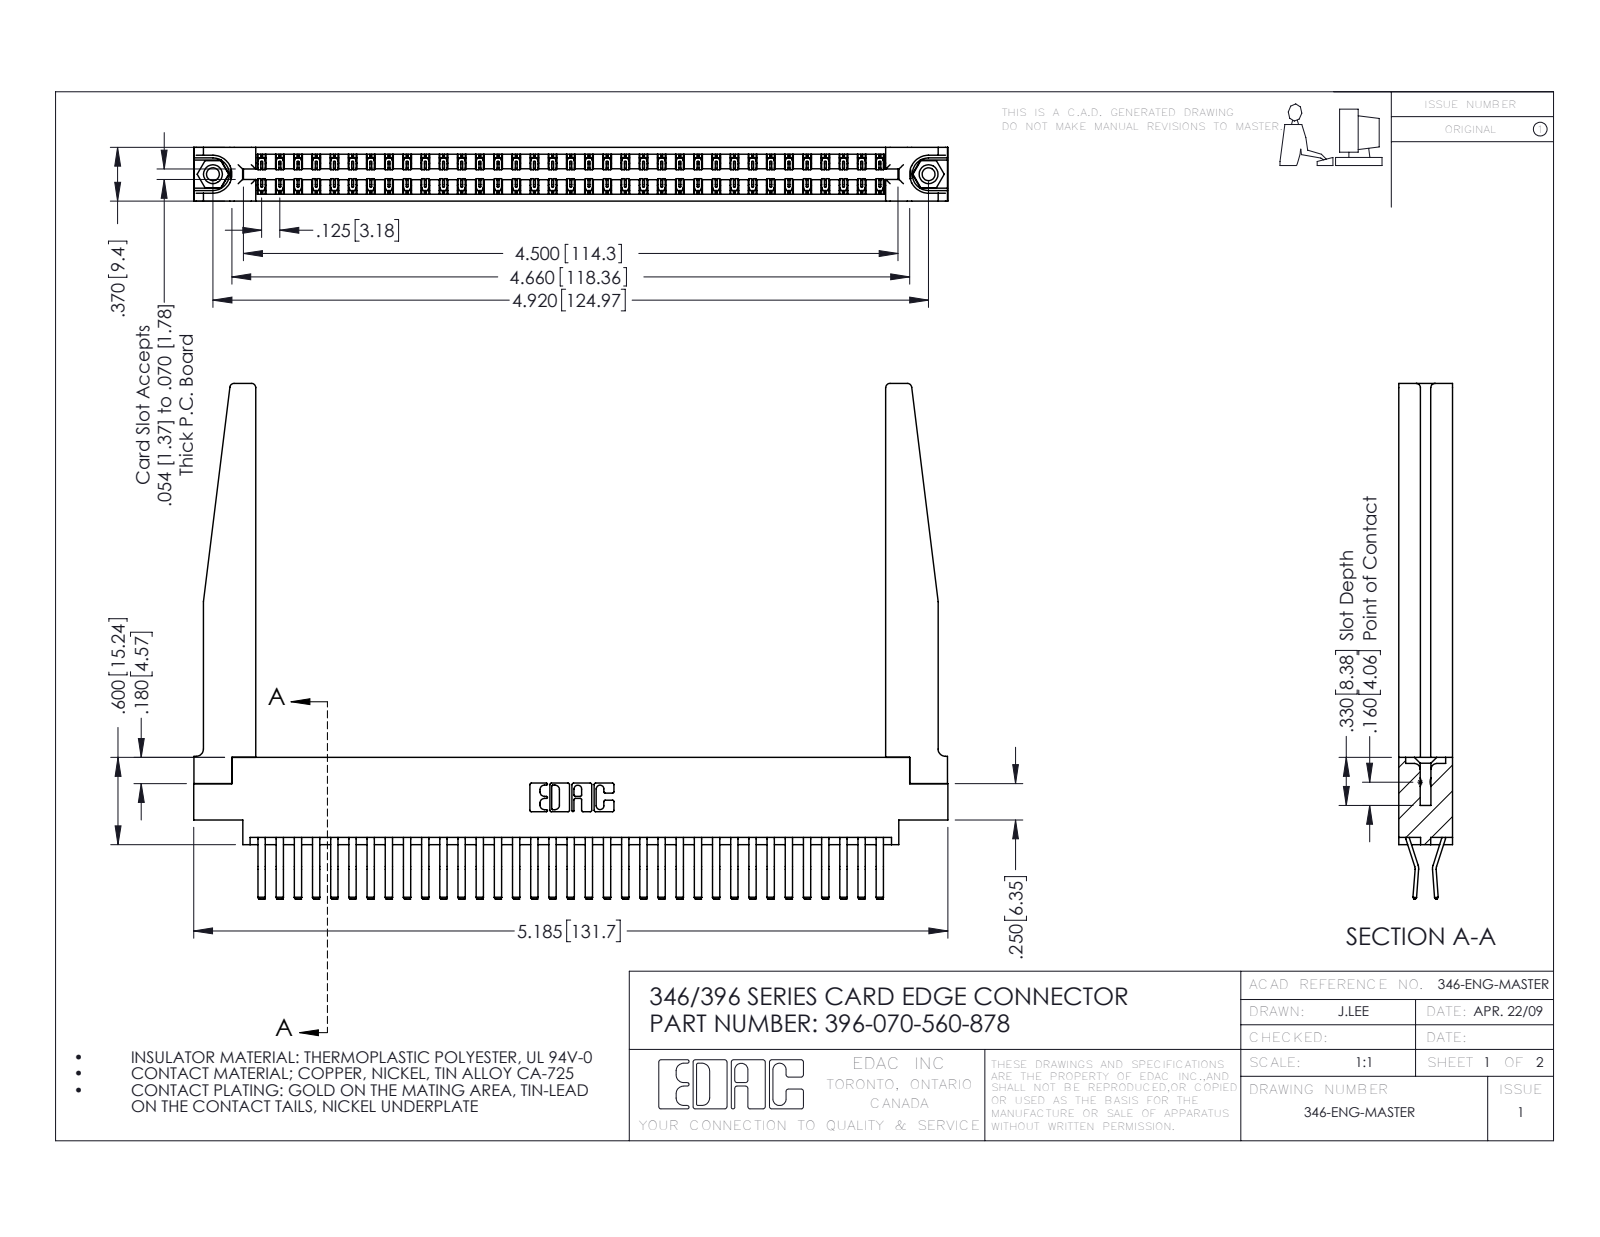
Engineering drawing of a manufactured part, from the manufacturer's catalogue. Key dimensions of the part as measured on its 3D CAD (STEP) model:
Part name (STEP PRODUCT): 346 Part_0.170 Offset - 0.156 Dia-TH; 346-220-078_345-220-078; 345-292-001_560 Tail; 345-250-001_345-250-001-102 (+1 more)
STEP written by: SolidWorks 2016 (CONFIG_CONTROL_DESIGN)
Units: inches
Bodies: 75 solids, 4140 faces (2672 planar, 1416 cylindrical, 52 other)
Overall size (bounding box): 5.185 × 3.545 × 0.37
Volume: 1.221 in³ · Surface area: 40.03 in²
Round holes (diameter × count): ⌀0.089 ×2, ⌀0.125 ×2, ⌀0.156 ×2, ⌀0.064 ×1
Round bosses / shafts (diameter × count): ⌀0.155 ×2
Partial cylindrical surfaces — rounded edges, fillets, slot ends (radius × count): R0.006 ×105, R0.01 ×22, R0.03 ×8, R0.007 ×6, R0.031 ×6, R0.05 ×4, R0.026 ×3, R0.01 ×2
Main face-to-face distances: 0.37, 0.048, 0.322, 0.072, 0.025, 0.148, 0.15, 0.25, 0.298, 0.275
Hole centre spacings: 0.246, 4.711, 4.92
